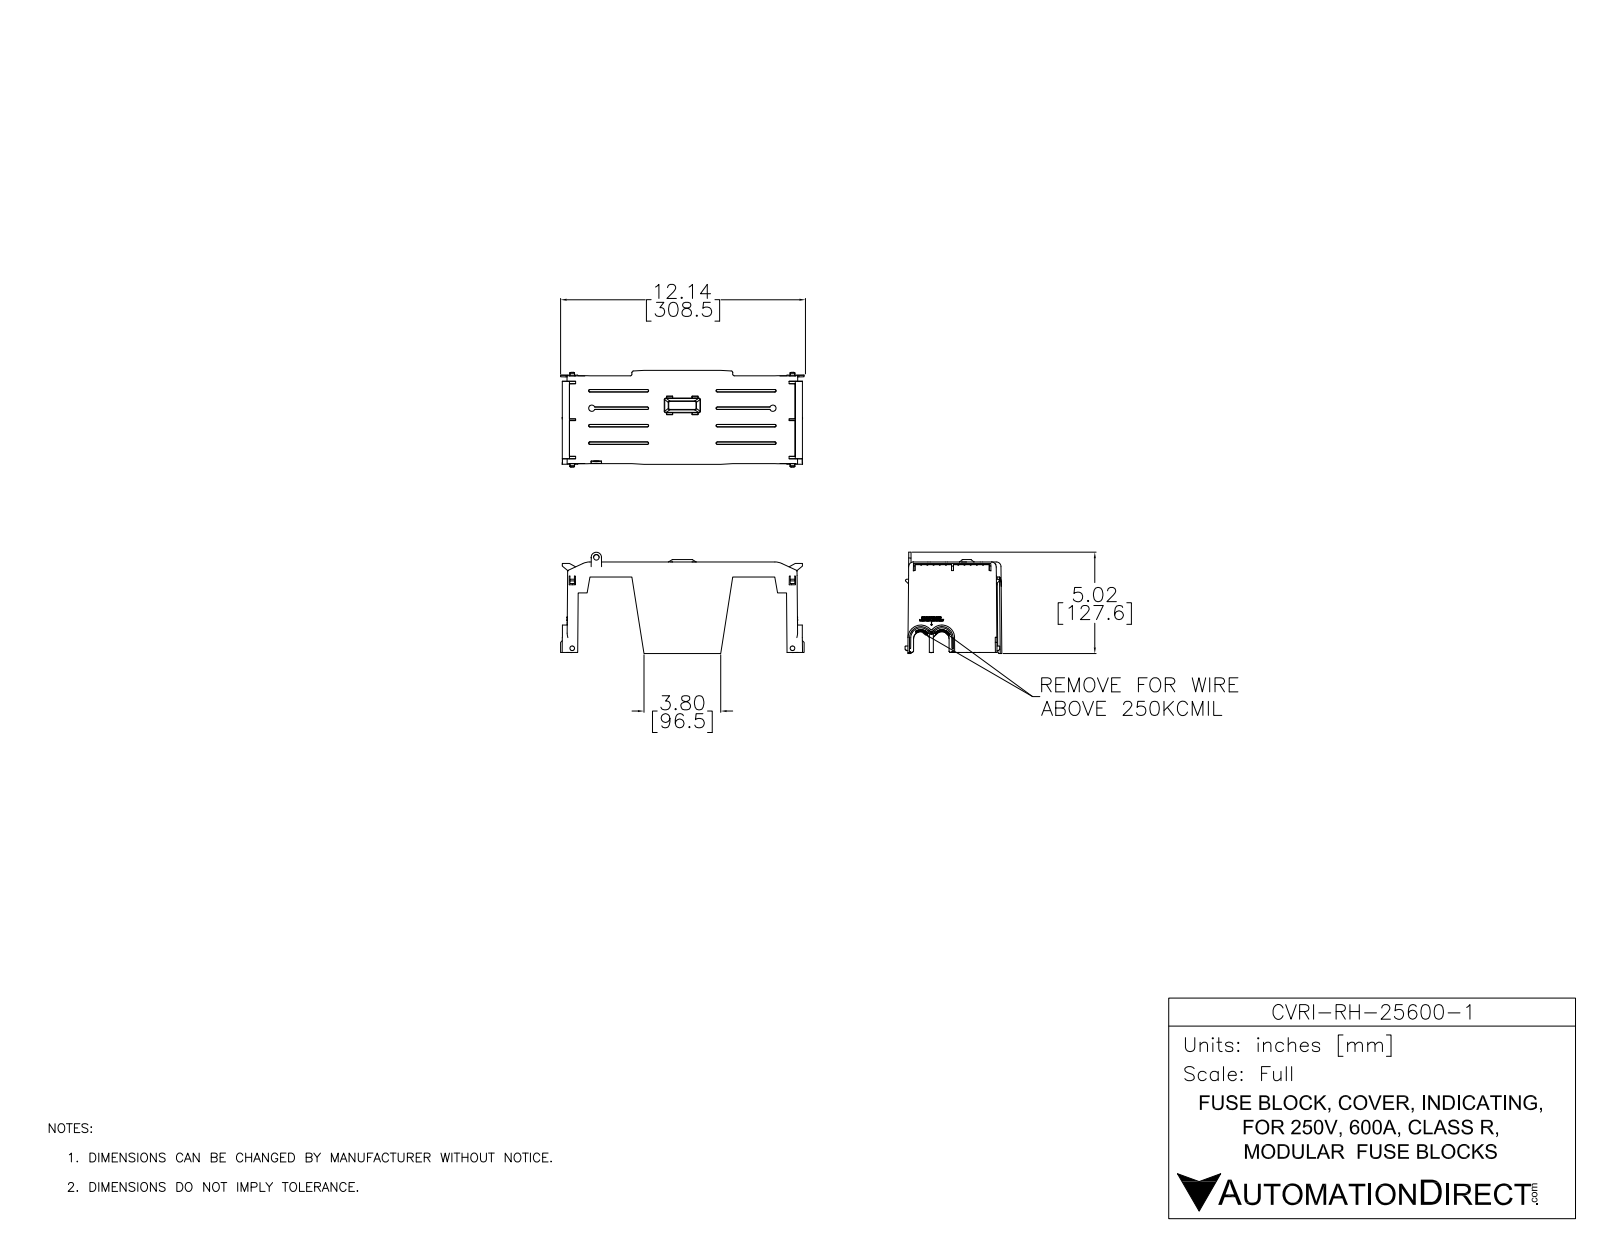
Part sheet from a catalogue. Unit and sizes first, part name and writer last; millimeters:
Units: millimetres
Overall size (bounding box): 306.7 × 127.7 × 121.8
Round holes (diameter × count): ⌀7 ×1
Partial cylindrical surfaces — rounded edges, fillets, slot ends (radius × count): R1 ×18, R4 ×9, R3 ×8, R6 ×7, R2 ×4, R9 ×4, R12.5 ×4, R14 ×4
Main face-to-face distances: 2, 6, 4, 8, 5, 3, 20.2, 64, 4, 22
Volume: 211 900 mm³ · Surface area: 215 100 mm²
Bodies: 1 solid, 2344 faces (1576 planar, 119 cylindrical, 649 other)
Part name (STEP PRODUCT): CVRI-RH-25600-1
STEP written by: SolidWorks 2017 (AUTOMOTIVE_DESIGN)
